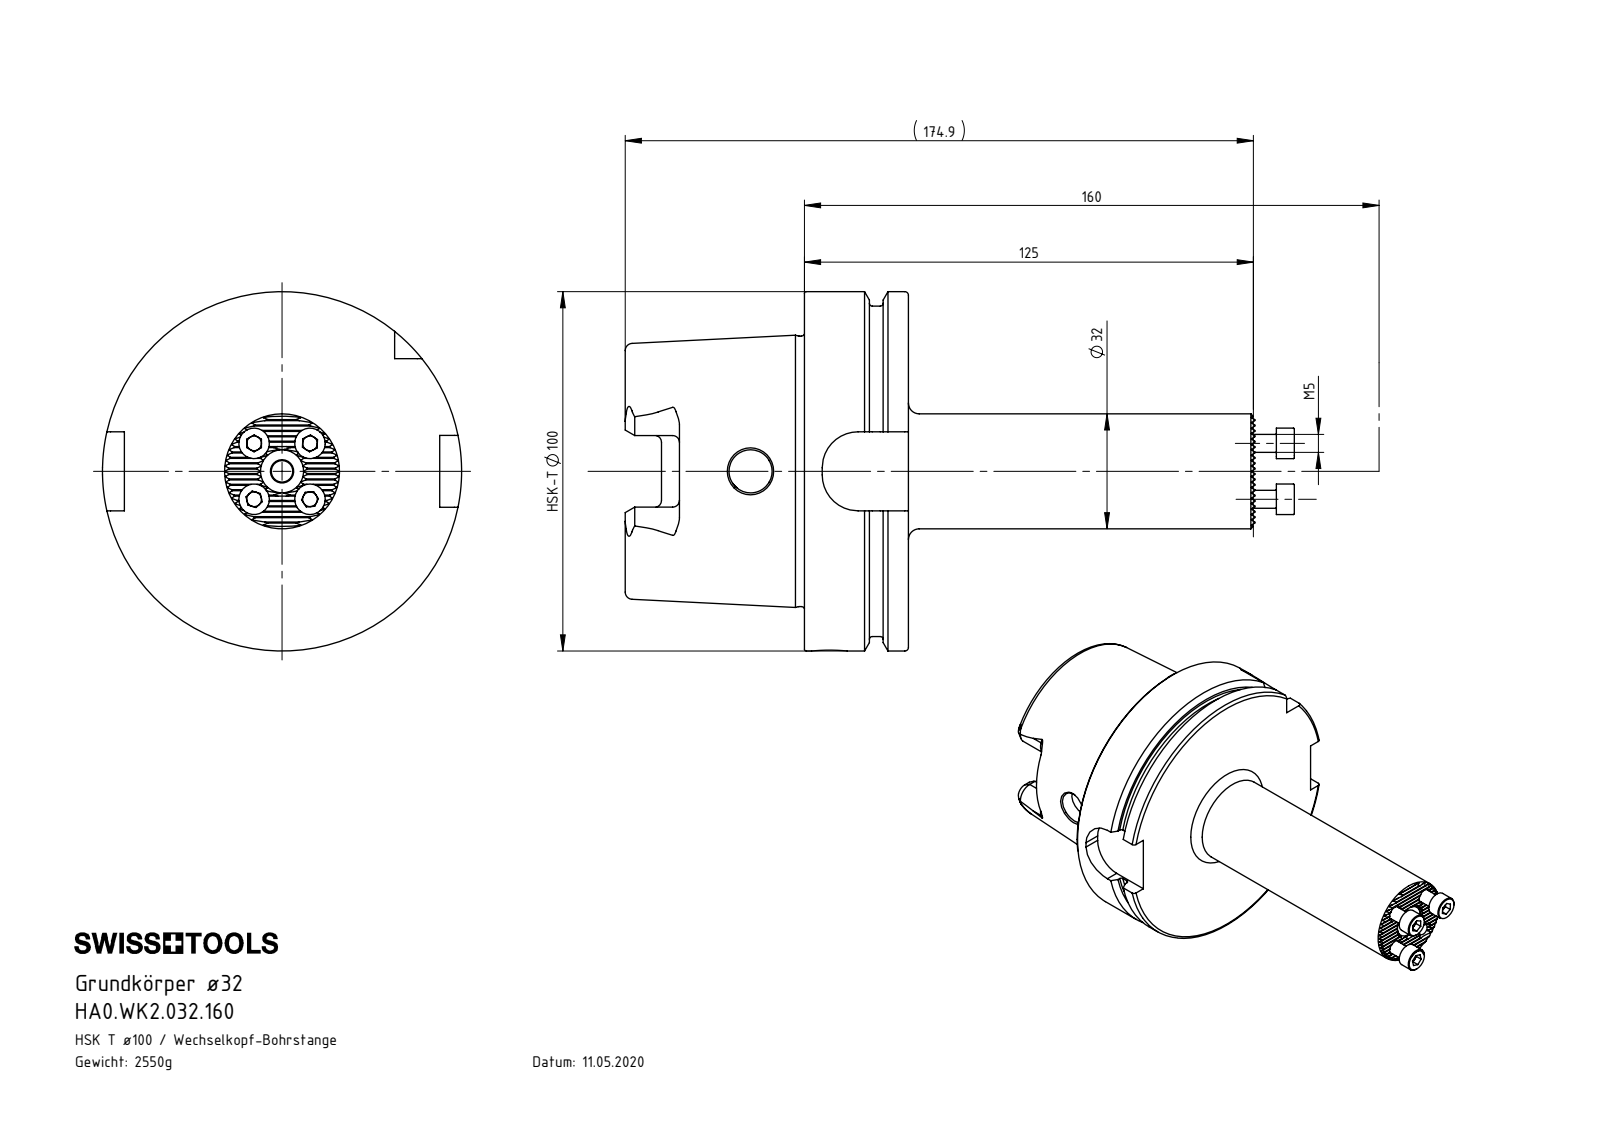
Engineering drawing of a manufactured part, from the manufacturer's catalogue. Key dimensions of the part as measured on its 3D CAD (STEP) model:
Part name (STEP PRODUCT): HA0-WK2.032.160_A; HA0-WK2.032.160; ISO 4762 - M5 x 14; DIN 3771 - 6x1
STEP written by: SolidWorks 2017 (CONFIG_CONTROL_DESIGN)
Units: millimetres
Bodies: 6 solids, 471 faces (232 planar, 118 cylindrical, 121 other)
Overall size (bounding box): 186.3 × 100 × 100
Volume: 326 768 mm³ · Surface area: 64 710 mm²
Round holes (diameter × count): ⌀4.2 ×4, ⌀6 ×1, ⌀7.4 ×1, ⌀8.5 ×1, ⌀10 ×1, ⌀12 ×1, ⌀22.5 ×1, ⌀26 ×1, ⌀53 ×1, ⌀63 ×1
Round bosses / shafts (diameter × count): ⌀8.5 ×4, ⌀5 ×4, ⌀100 ×1, ⌀91.95 ×1, ⌀75.26 ×1, ⌀32 ×1
Partial cylindrical surfaces — rounded edges, fillets, slot ends (radius × count): R0.12 ×21, R1.9 ×6, R4.88 ×4, R10 ×4
Main face-to-face distances: 28.95, 12.45, 16.5, 49.9, 62.35, 78.85, 1.3, 2.6, 78.2, 28.3
Hole centre spacings: 11, 15.56, 22.01
